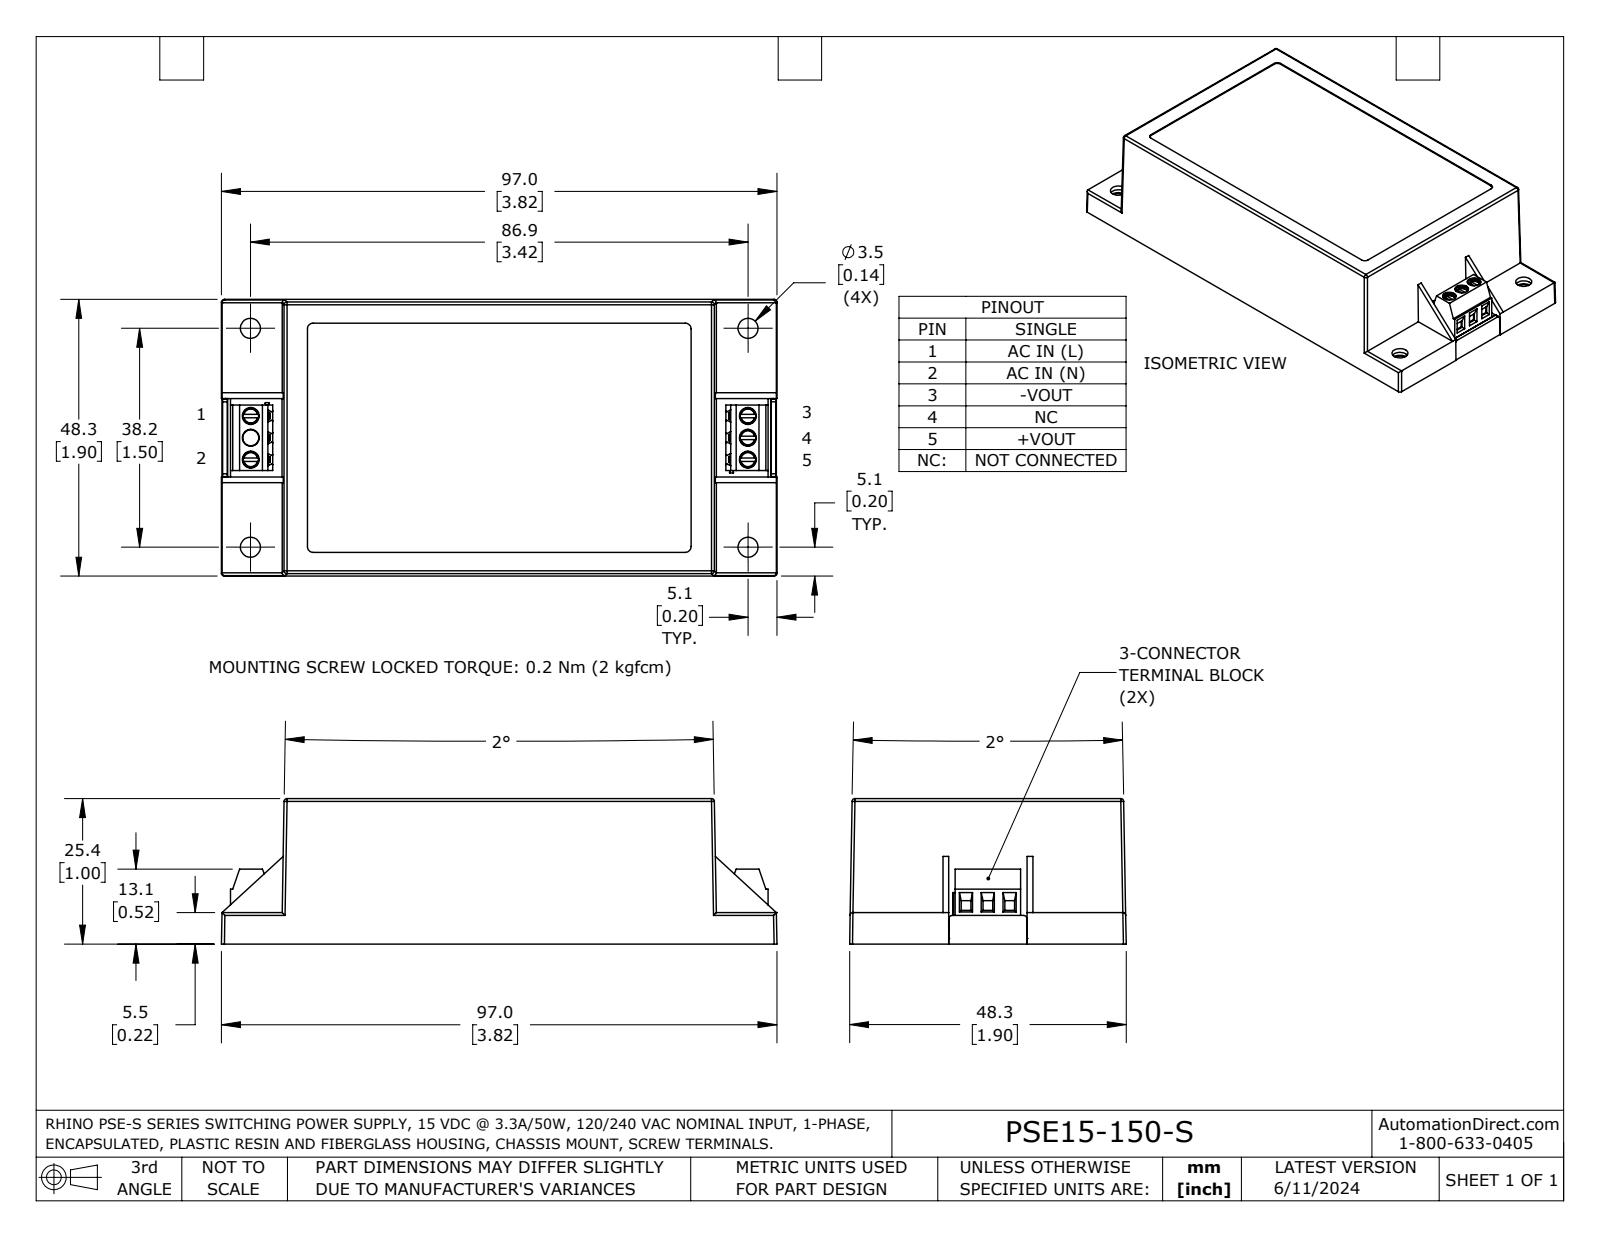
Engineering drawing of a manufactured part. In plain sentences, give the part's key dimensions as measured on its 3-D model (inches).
The part is named "PSE15-150-S". Its 3-D file was written by "SolidWorks 2023 (AUTOMOTIVE_DESIGN)". It is 5 solids with 560 faces: 396 planar, 130 cylindrical and 34 other. Overall it measures 3.819 by 1.902 by 1 inches. Its volume is 1.175 cubic inches and its surface area 63.85 square inches. Round holes: 6 of diameter 0.116, 4 of diameter 0.138, 4 of diameter 0.161, 1 of diameter 0.11. Partial cylindrical surfaces (rounded edges, fillets, slot ends): 18 of radius 0.009, 18 of radius 0.02, 12 of radius 0.006, 8 of radius 0.004, 4 of radius 0.008, 4 of radius 0.01, 4 of radius 0.039, 4 of radius 0.079. The main face-to-face distances are 0.039, 0.138, 0.815, 0.953, 0.177, 0.098, 0.776, 0.913, 0.854, 0.992. The hole center spacings are 0.15, 3.42, 3.417, 0.3, 0.602, 0.602, 0.752, 0.752.
